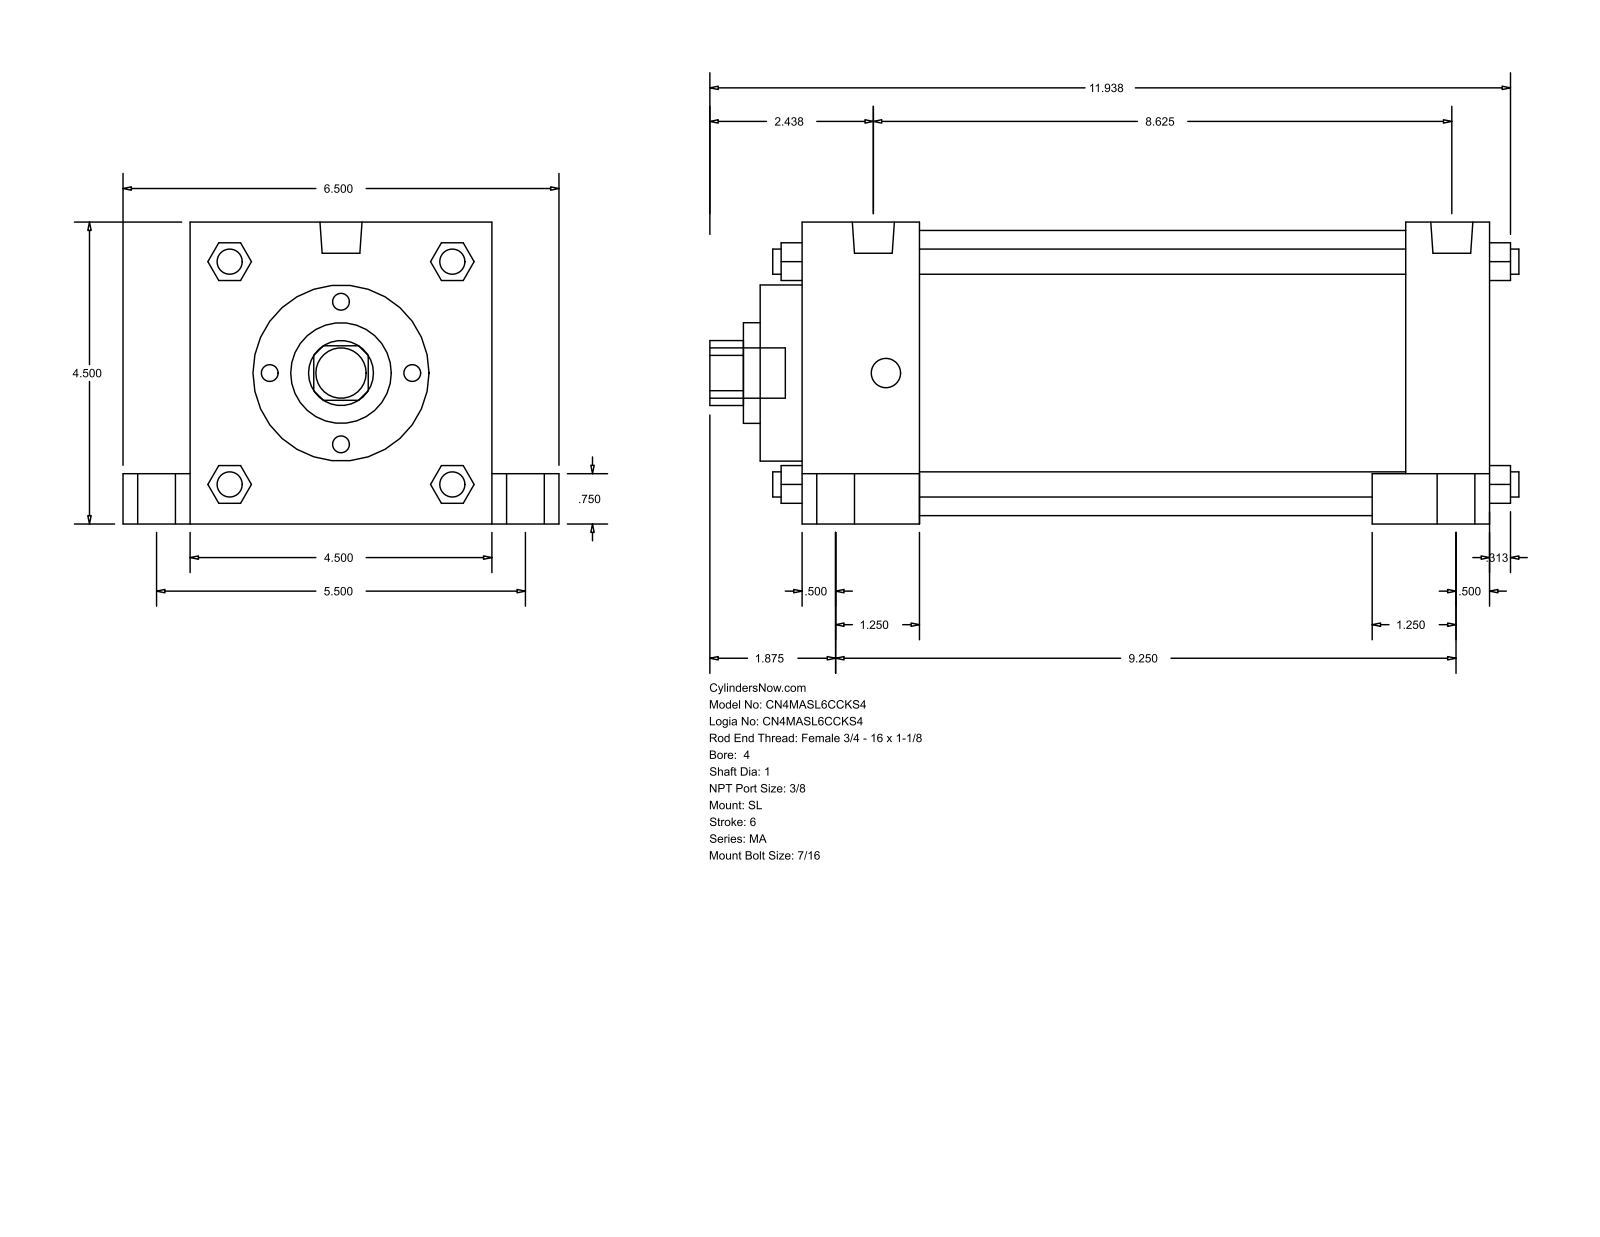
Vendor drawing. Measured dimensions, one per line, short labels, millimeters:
name: MA_SL__0400_1
written by: GSSL Pune (CONFIG_CONTROL_DESIGN)
unit: mm
bodies: 0 solids, 150 faces (113 planar, 37 cylindrical, 0 other)
size: 306.39 × 165.1 × 114.3
holes: 1× ⌀25.4, 1× ⌀38.1, 1× ⌀66.67, 1× ⌀107.95
bosses: 4× ⌀20.64, 4× ⌀14.29, 4× ⌀11.11, 4× ⌀9.53, 2× ⌀15.93, 1× ⌀19.05
rounds: 1× R12.29
face distances: 114.3, 260.35, 44.46, 215.89, 228.6, 184.14, 31.75, 25.4, 139.7, 276.22
